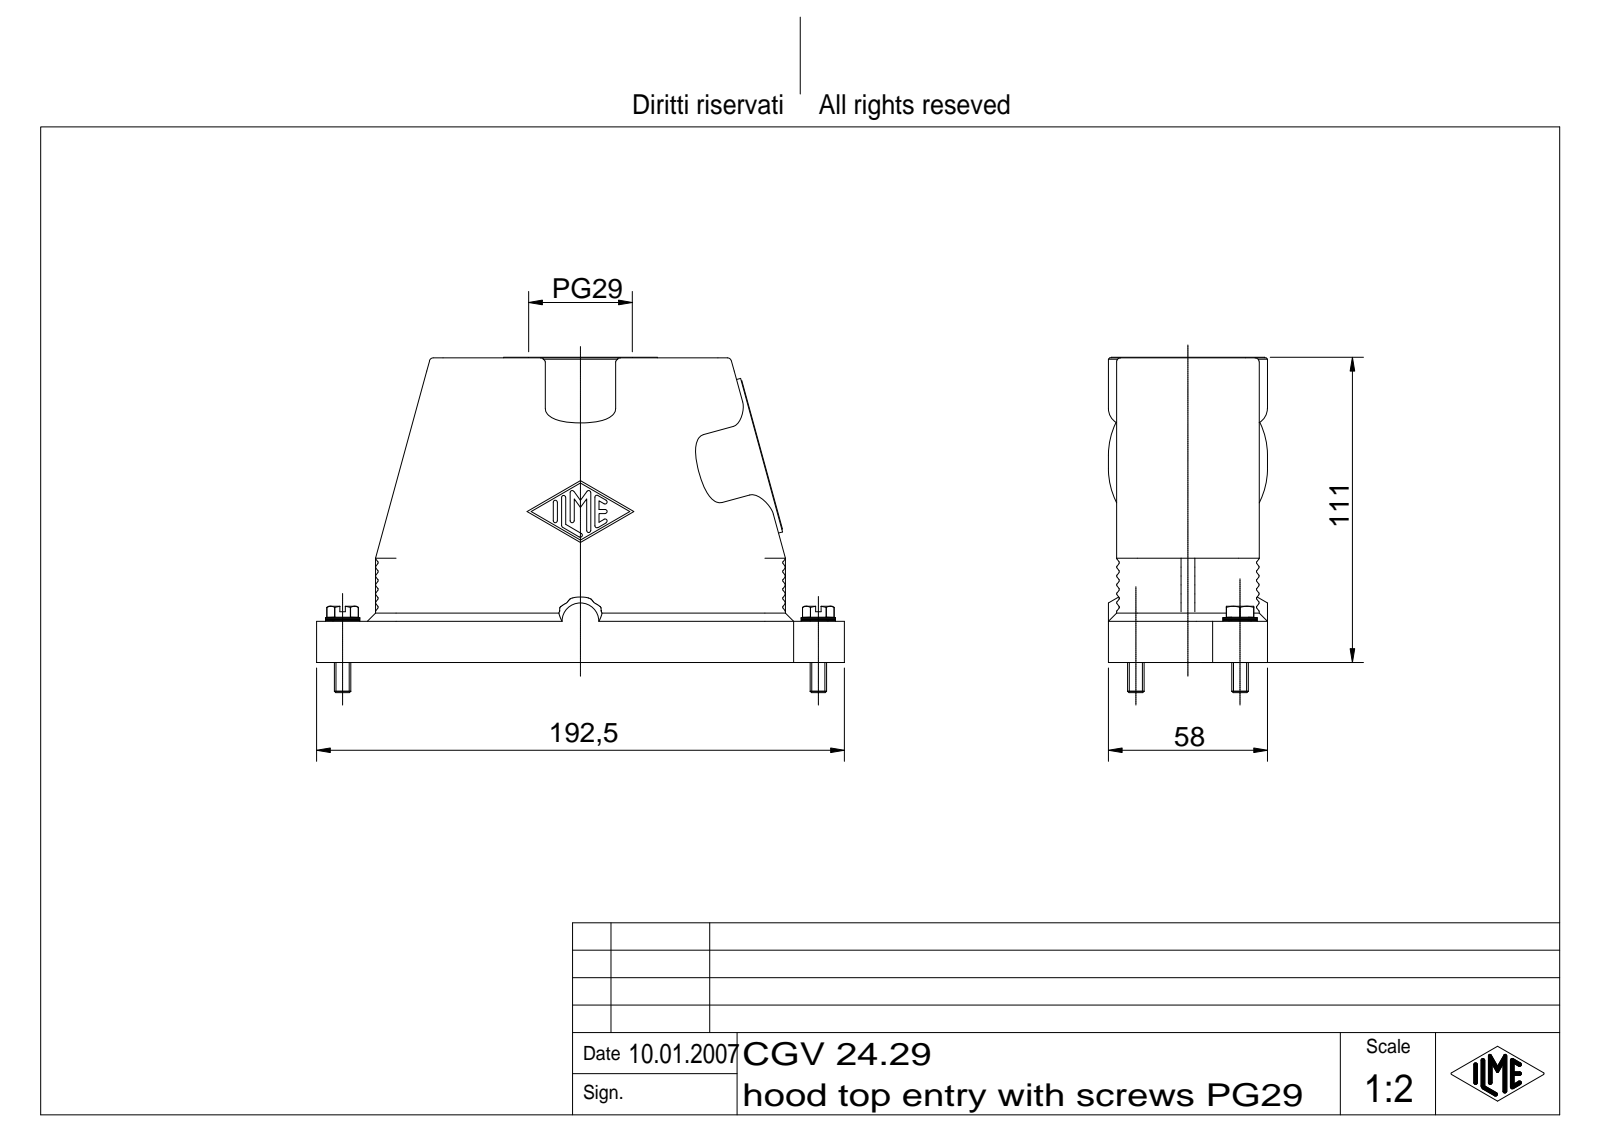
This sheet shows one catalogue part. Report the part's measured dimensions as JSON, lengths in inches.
{"part_name": "CGV 24.29", "step_written_by": "Autodesk Inventor 7 (AUTOMOTIVE_DESIGN)", "units": "inches", "bodies": {"solids": 3, "faces": 767, "planar": 189, "cylindrical": 195, "other": 383}, "overall_size": [7.579, 4.811, 2.283], "volume_in3": 15.37, "surface_area_in2": 166.5, "round_holes": [[0.097, 2], [0.126, 2], [0.26, 2], [0.591, 2], [1.397, 1]], "round_bosses_or_shafts": [[2.283, 2], [2.205, 2], [0.492, 2], [0.236, 2]], "partial_cylinders_radius": [[0.02, 39], [0.03, 14], [0.295, 8], [0.236, 6], [0.059, 4], [0.118, 4], [0.226, 2], [0.413, 2]], "face_to_face_distances": [0.118, 2.047, 1.929, 1.811, 0.236, 2.165, 0.098, 0.02, 2.283, 0.138], "hole_center_spacings": [1.385, 5.611, 4.23, 6.993]}
